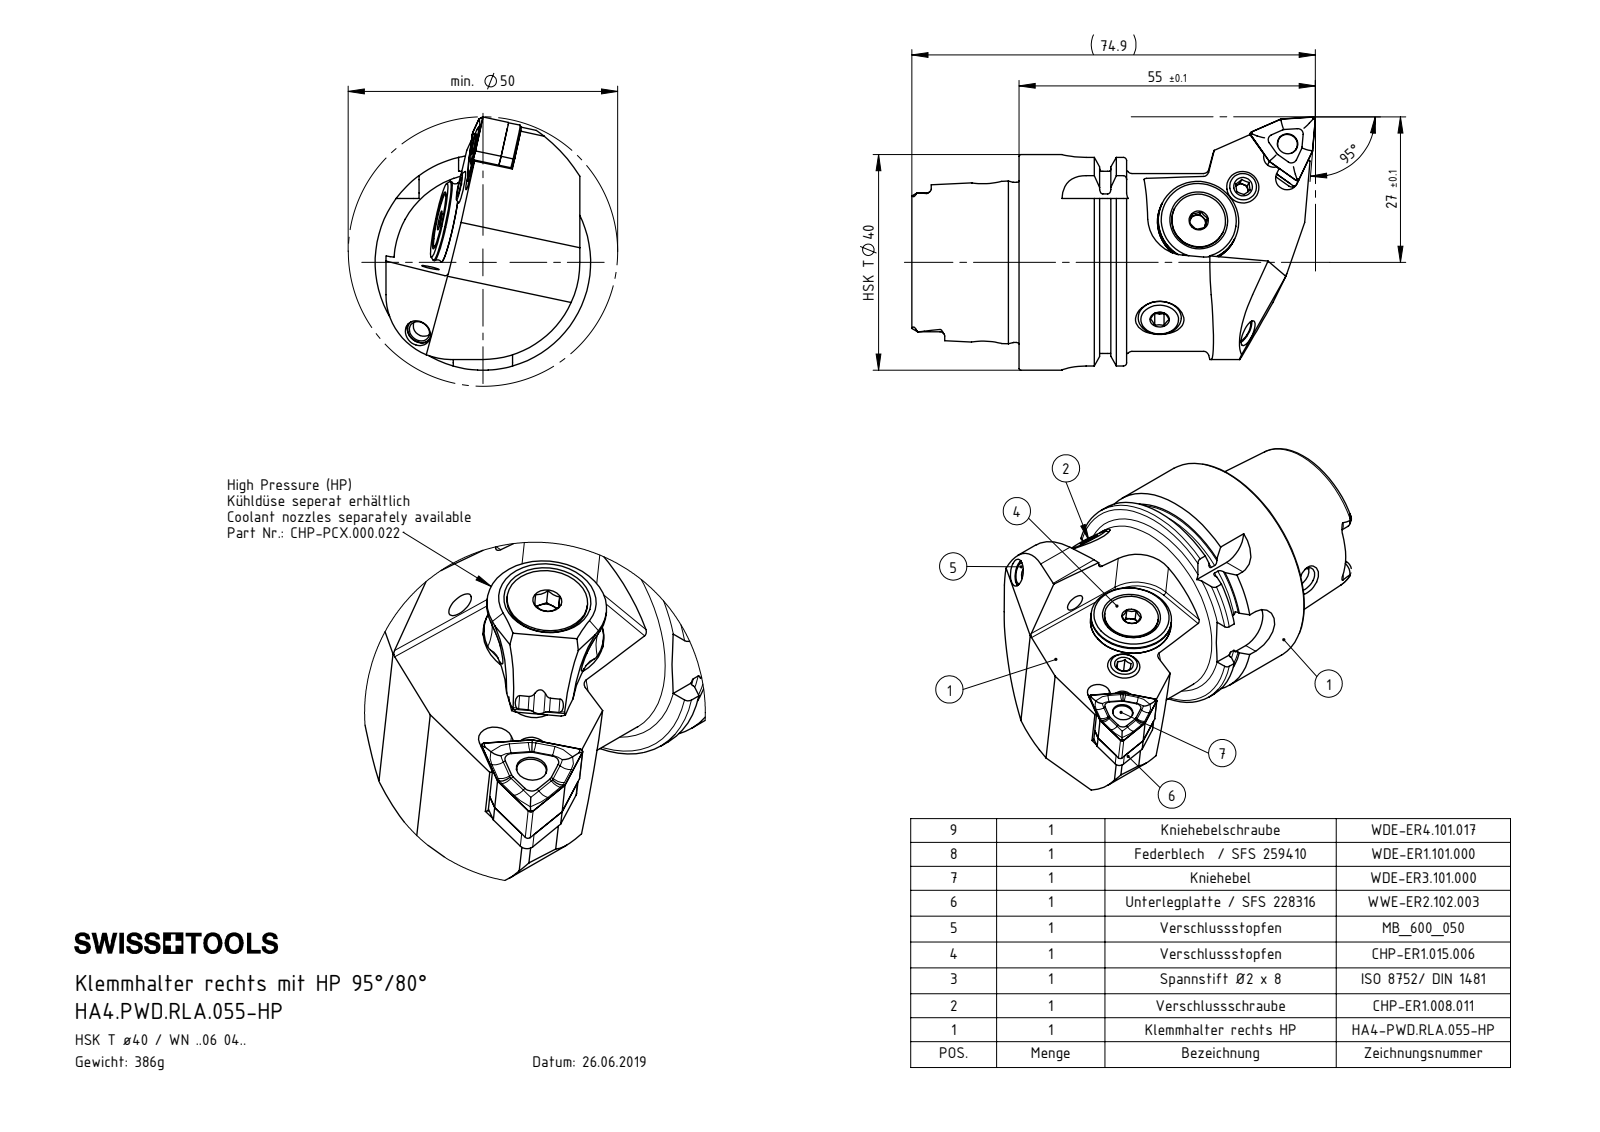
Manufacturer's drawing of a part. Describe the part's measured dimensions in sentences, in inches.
The part is named "CHP-ER1.008.011_A; WDE-ER3.101.000_A; DIN 7991 - M5x18; CHP-PCX.000.022_B (+8 more)". Its 3-D file was written by "SolidWorks 2017 (AUTOMOTIVE_DESIGN)". It is 14 solids with 660 faces: 197 planar, 174 cylindrical and 289 other. Overall it measures 2.949 by 1.85 by 1.575 inches. Its volume is 3.002 cubic inches and its surface area 30.27 square inches. Round holes: 4 of diameter 0.165, 3 of diameter 0.197, 1 of diameter 0.047, 1 of diameter 0.079, 1 of diameter 0.118, 1 of diameter 0.13, 1 of diameter 0.15, 1 of diameter 0.157, 1 of diameter 0.181, 1 of diameter 0.205, 1 of diameter 0.209, 1 of diameter 0.24. Round bosses or shafts: 2 of diameter 0.197, 1 of diameter 1.575, 1 of diameter 1.368, 1 of diameter 1.299, 1 of diameter 1.17, 1 of diameter 0.585, 1 of diameter 0.528, 1 of diameter 0.394. Partial cylindrical surfaces (rounded edges, fillets, slot ends): 10 of radius 0.039, 6 of radius 0.035, 4 of radius 0.02, 4 of radius 0.074, 4 of radius 0.177, 3 of radius 0.016, 3 of radius 0.083, 3 of radius 0.236. The main face-to-face distances are 0.313, 0.785, 0.472, 0.177, 0.181, 0.783, 1.096, 1.569, 0.059, 0.102. The hole center spacings are 0.177, 0.764, 0.177, 0.178, 0.322, 0.322, 0.428, 0.429.
